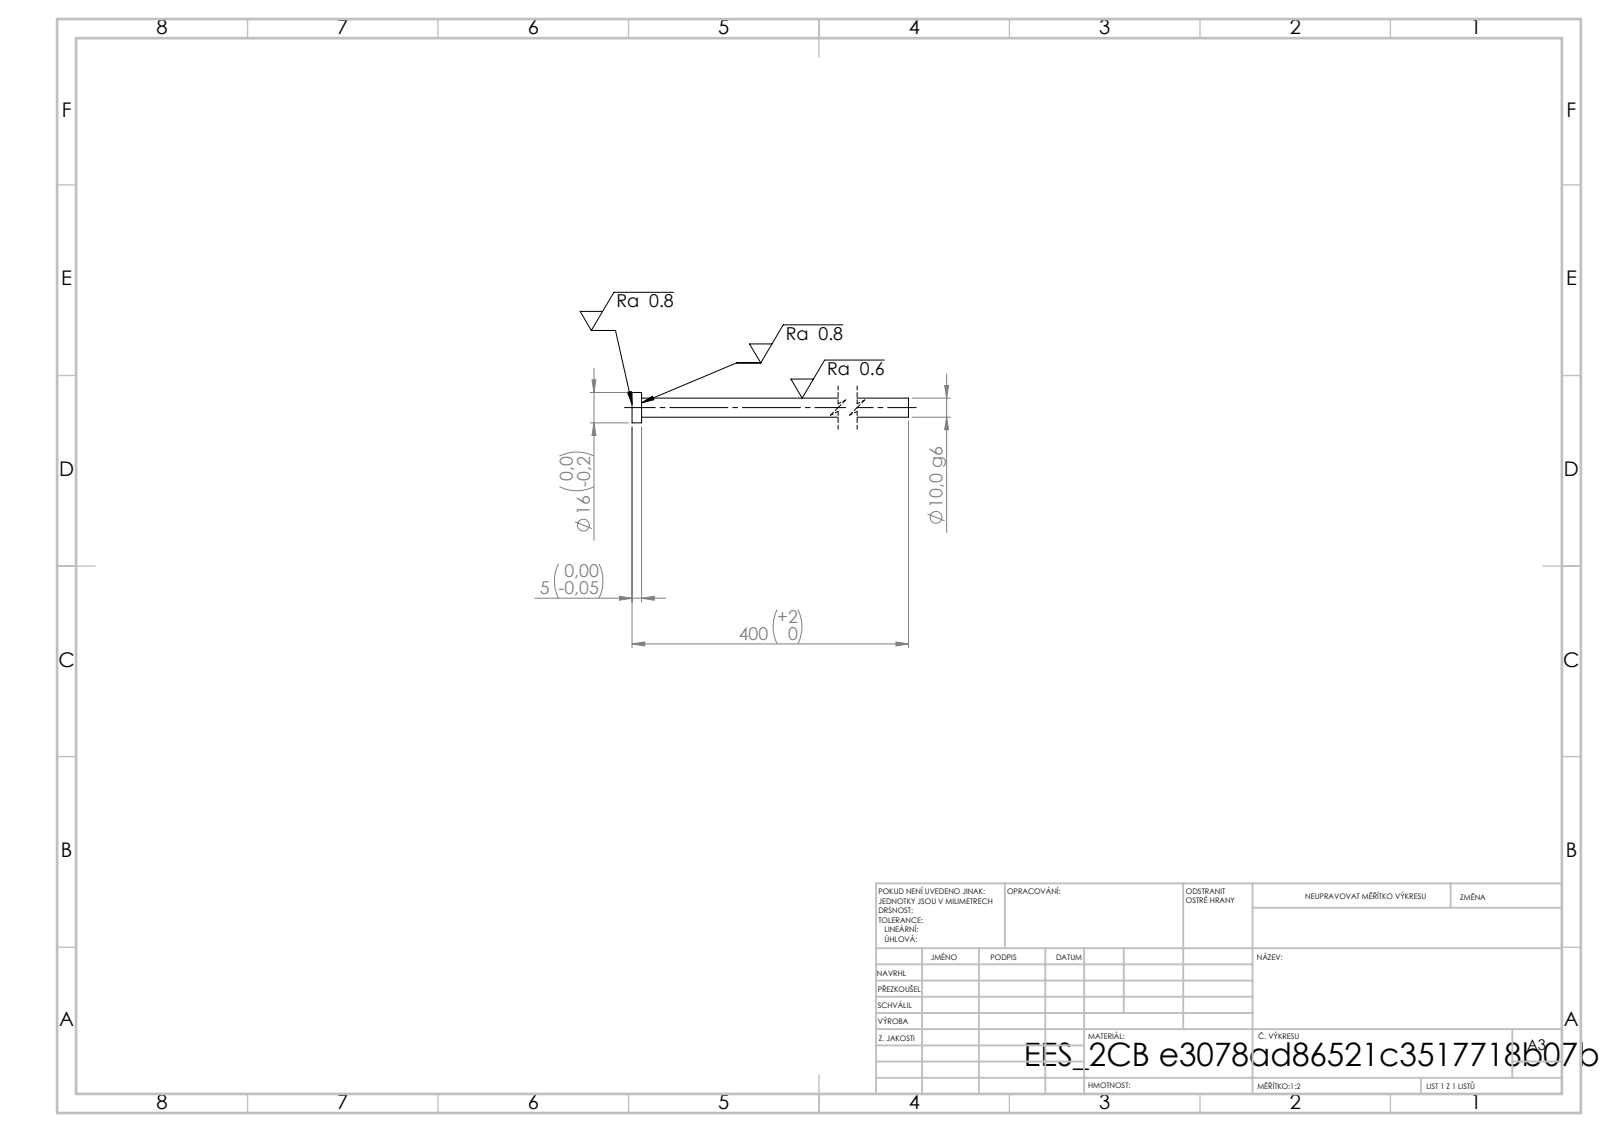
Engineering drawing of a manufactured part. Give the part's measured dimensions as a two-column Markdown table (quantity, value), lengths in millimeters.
| quantity | value |
| --- | --- |
| STEP written by | SolidWorks 2019 (CONFIG_CONTROL_DESIGN) |
| units | millimeters |
| bodies | 1 solid, 7 faces (3 planar, 4 cylindrical, 0 other) |
| overall size | 400 × 16 × 16 |
| volume | 32 029 mm³ |
| surface area | 13 063 mm² |
| round bosses / shafts (diameter × count) | 16 × 1, 10 × 1 |
| main face-to-face distances | 5, 400, 395 |
